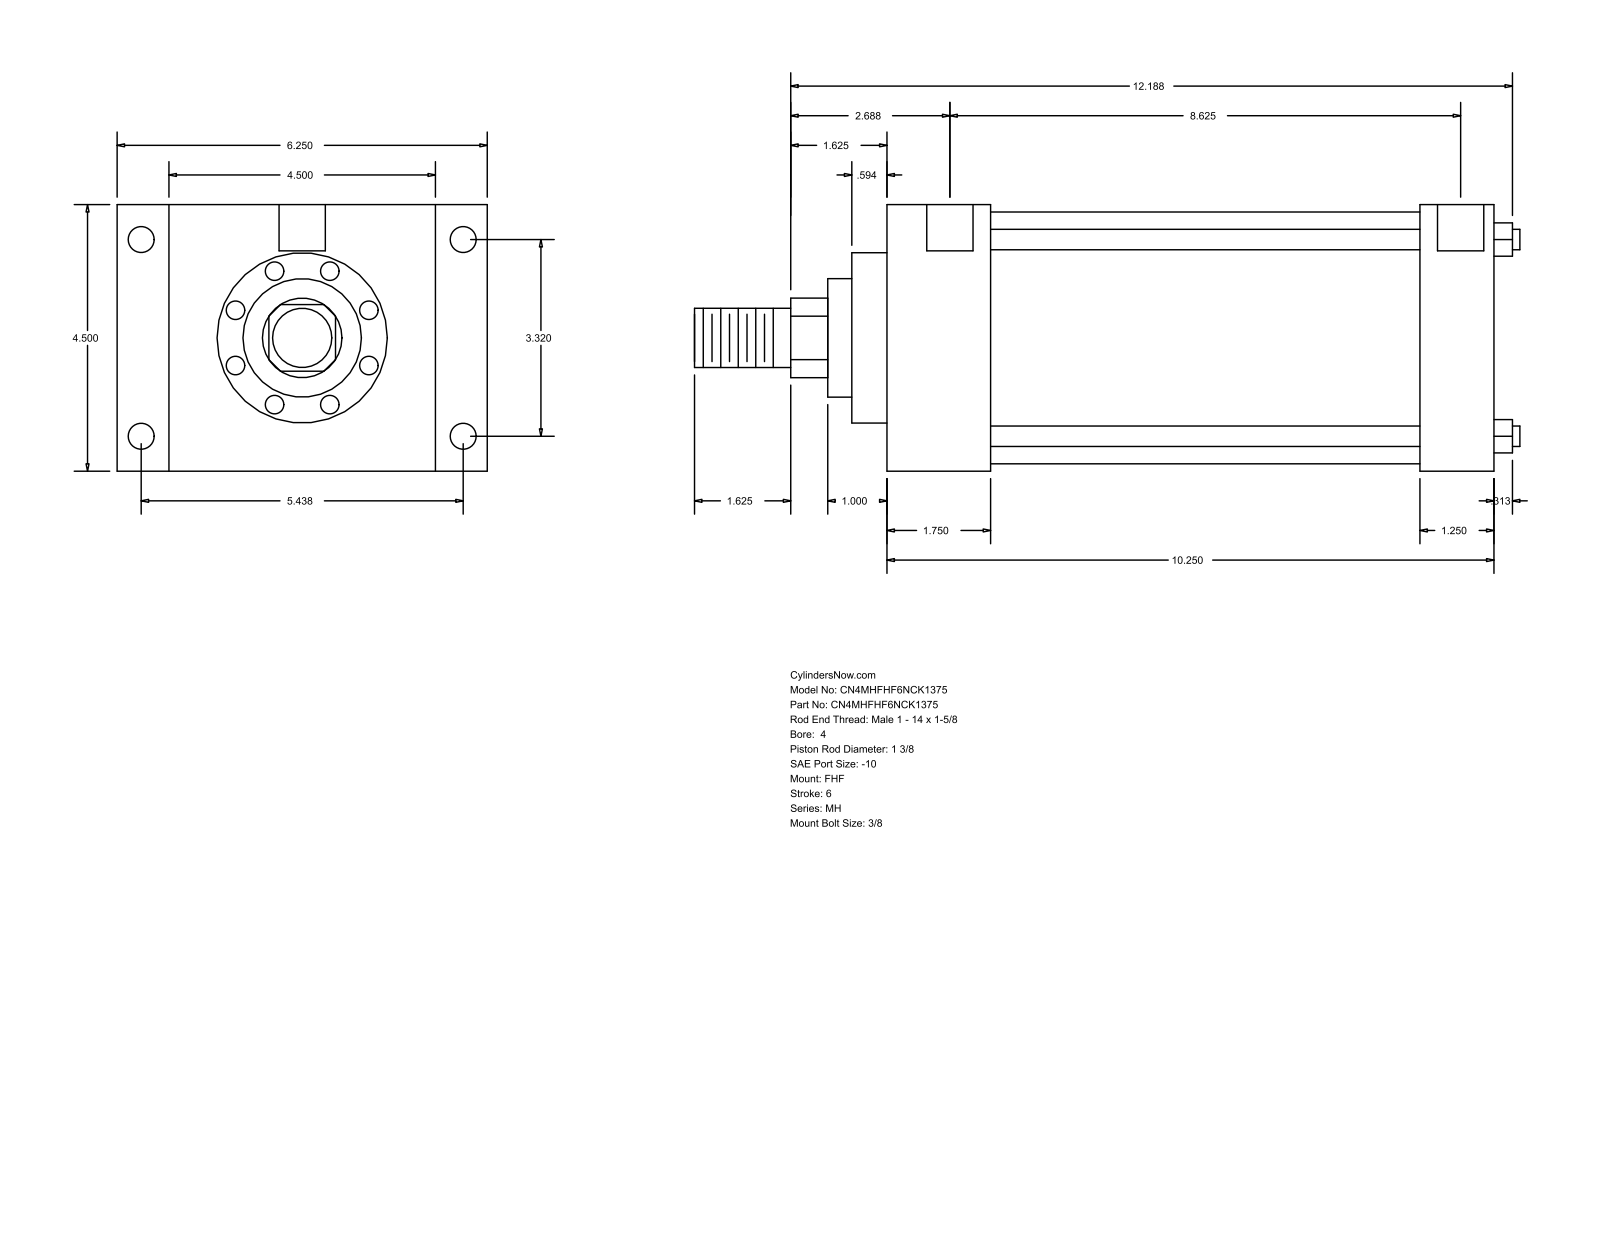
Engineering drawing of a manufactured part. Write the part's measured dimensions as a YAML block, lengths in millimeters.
part_name: "MH_FHF__0400_1.375"
step_written_by: "GSSL Pune (CONFIG_CONTROL_DESIGN)"
units: millimeters
bodies: {solids: 0, faces: 90, planar: 61, cylindrical: 29, other: 0}
overall_size: [354.01, 158.75, 114.3]
round_holes:
  - {diameter: 8.73, count: 4}
  - {diameter: 11.13, count: 4}
  - {diameter: 19.84, count: 2}
round_bosses_or_shafts:
  - {diameter: 8.76, count: 4}
  - {diameter: 107.95, count: 1}
  - {diameter: 73.03, count: 1}
  - {diameter: 50.8, count: 1}
  - {diameter: 34.92, count: 1}
  - {diameter: 25.4, count: 1}
partial_cylinders:
  - {radius: 17.06, count: 1}
face_to_face_distances: [114.3, 260.35, 44.45, 215.9, 22.23, 136.53, 158.76, 228.61, 184.16, 31.74]
hole_center_spacings: [1.59, 84.32, 138.12, 161.82, 220.67, 222.26, 219.08]
